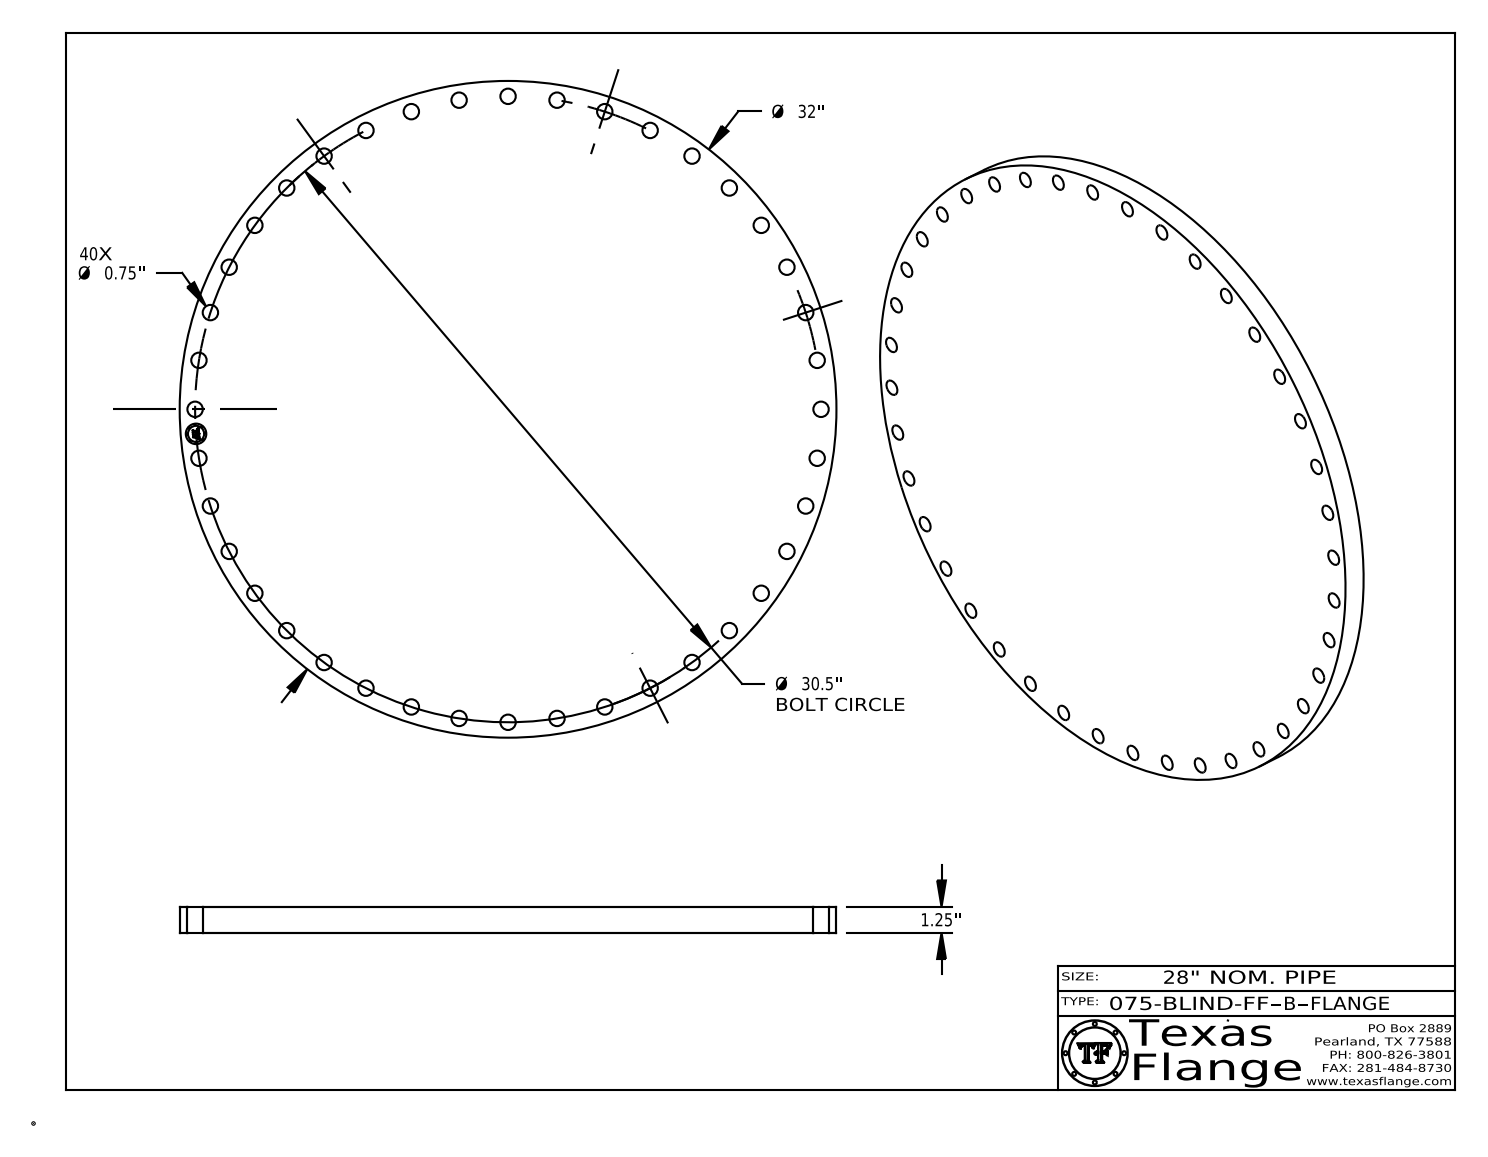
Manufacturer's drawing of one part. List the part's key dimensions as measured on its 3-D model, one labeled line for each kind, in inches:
Part name (STEP PRODUCT): 075-BLIND-FF, Series B
STEP written by: CATIA V5 STEP AP214 (AUTOMOTIVE_DESIGN)
Units: inches
Bodies: 1 solid, 469 faces (367 planar, 102 cylindrical, 0 other)
Overall size (bounding box): 32 × 32 × 1.25
Volume: 983.2 in³ · Surface area: 1 817 in²
Round holes (diameter × count): ⌀0.75 ×40, ⌀1 ×1
Round bosses / shafts (diameter × count): ⌀0.061 ×8, ⌀32 ×1, ⌀0.788 ×1
Main face-to-face distances: 1.25, 1.235, 0.015, 0.298, 0.293, 0.054, 0.193, 0.248, 0.044, 0.15
Hole centre spacings: 30.406, 30.124, 4.771, 29.007, 28.178, 26.006, 7.12, 29.657
